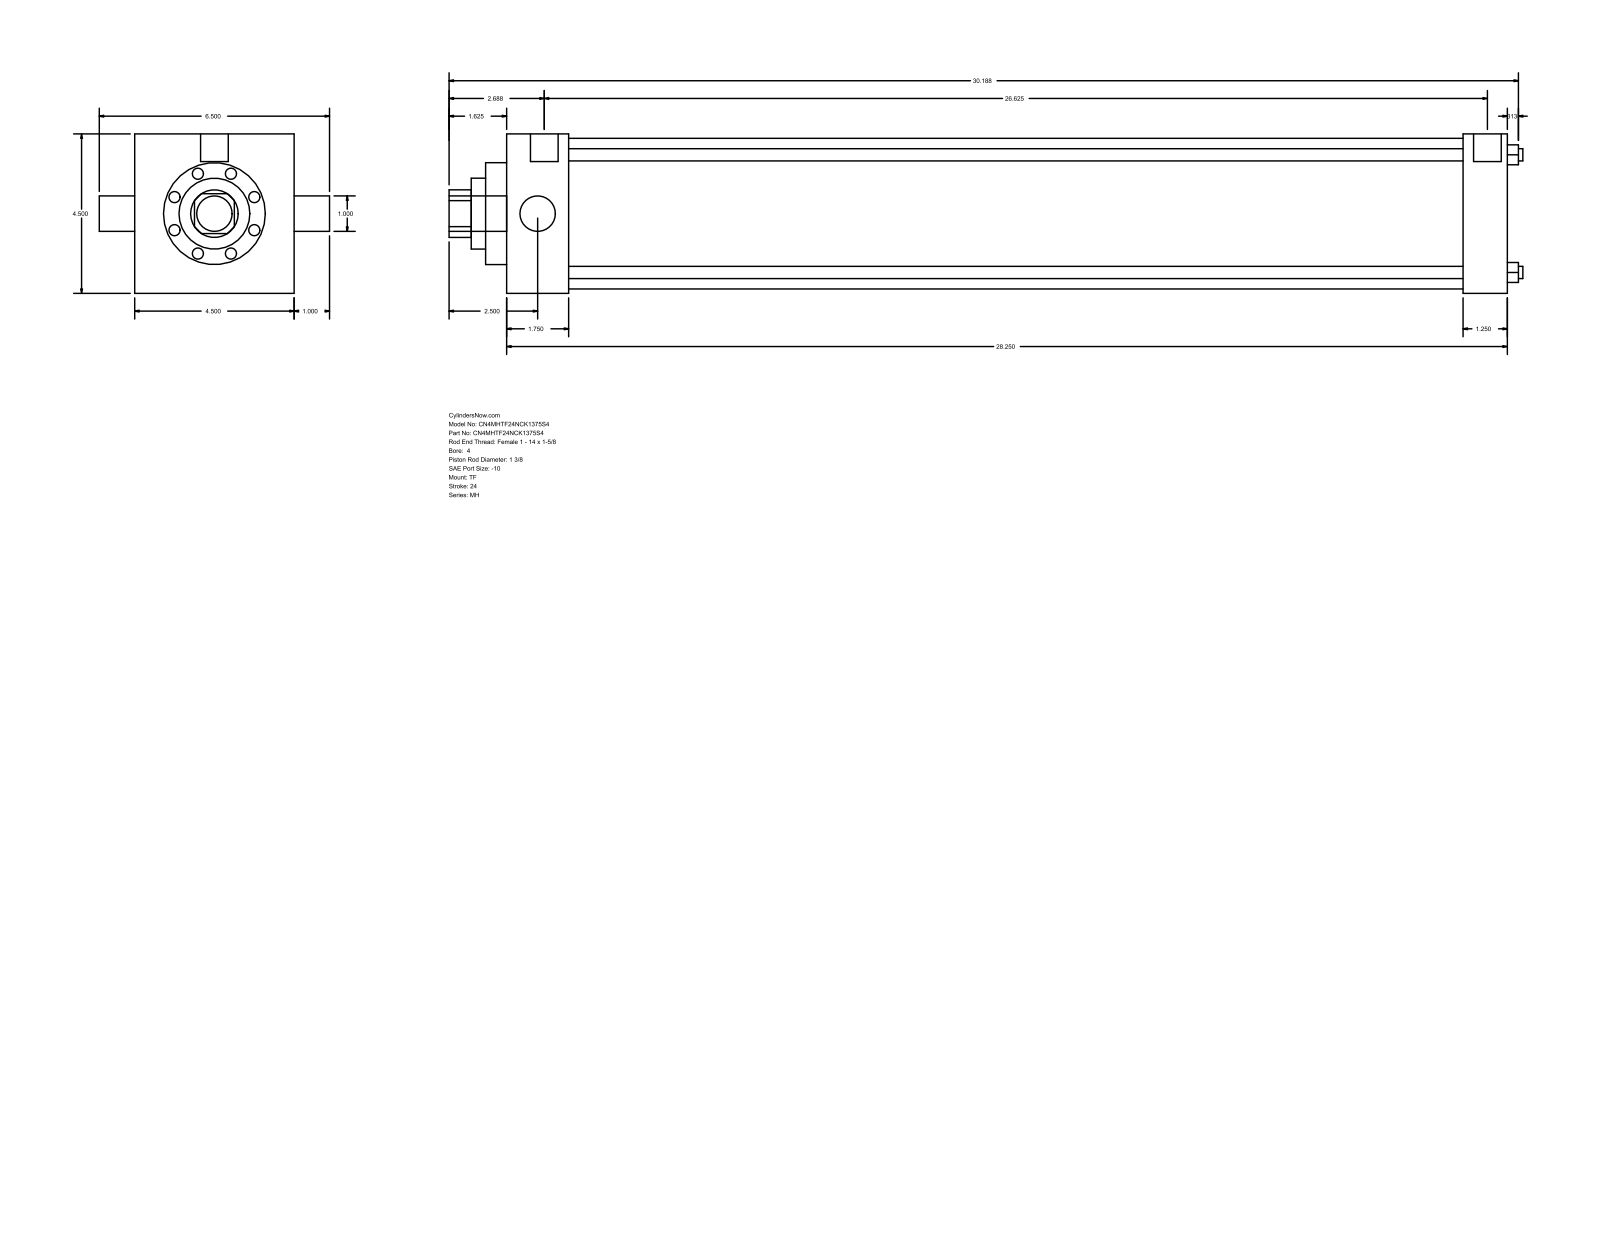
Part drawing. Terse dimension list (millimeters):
name: MH_TF__0400_1.375
written by: GSSL Pune (CONFIG_CONTROL_DESIGN)
unit: mm
bodies: 0 solids, 86 faces (61 planar, 25 cylindrical, 0 other)
size: 769.94 × 165.1 × 114.3
holes: 4× ⌀8.76, 1× ⌀25.4, 1× ⌀34.92, 1× ⌀50.8, 1× ⌀73.03, 1× ⌀107.95
bosses: 3× ⌀8.73, 2× ⌀19.84, 1× ⌀25.4
rounds: 1× R17.06
face distances: 114.3, 717.56, 44.45, 673.11, 685.81, 641.36, 31.75, 15.08, 59.53, 700.89
hole spacings: 59.62, 84.32, 119.25
